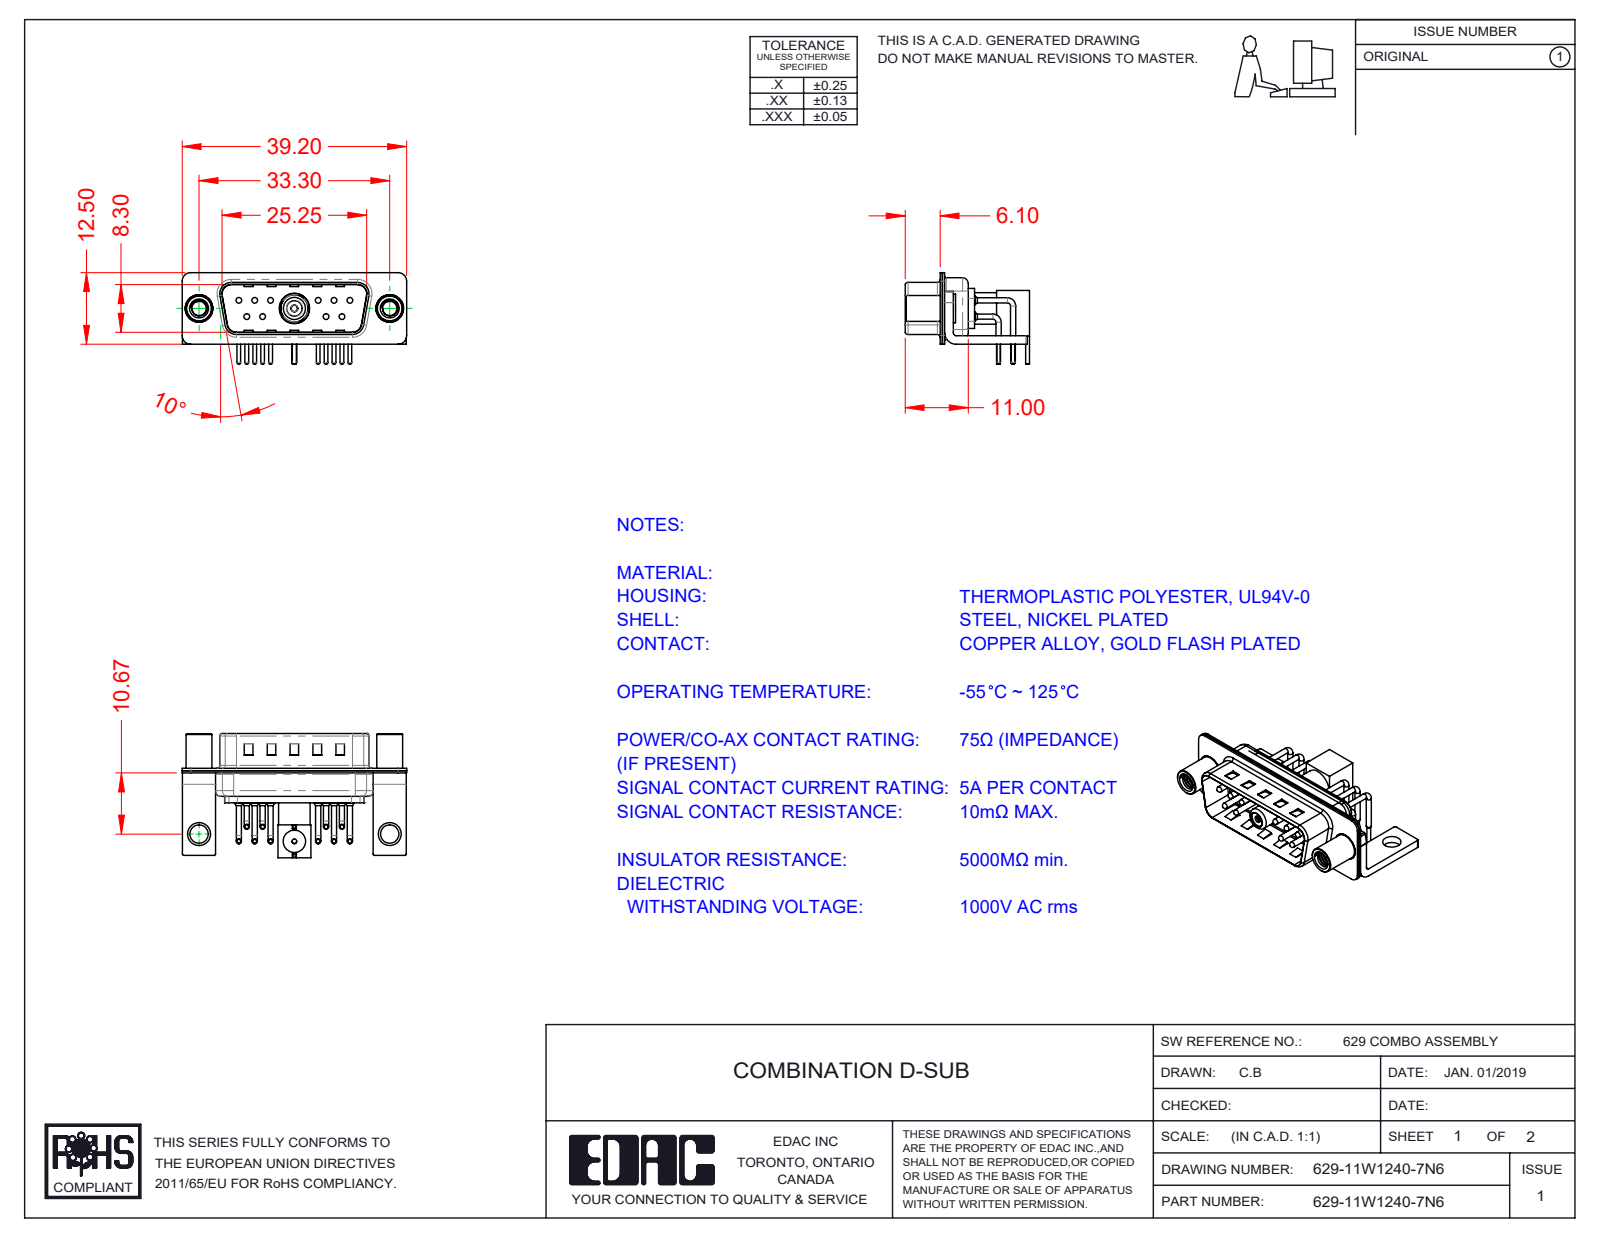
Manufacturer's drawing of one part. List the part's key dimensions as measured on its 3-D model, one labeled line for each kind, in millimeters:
Part name (STEP PRODUCT): Locking Collar; 629-11W1240-7N6; Socket_RA; Co-Ax Jack Assy_RA (+8 more)
STEP written by: SolidWorks 2020 (CONFIG_CONTROL_DESIGN)
Units: millimetres
Bodies: 24 solids, 1703 faces (867 planar, 636 cylindrical, 200 other)
Overall size (bounding box): 39.2 × 21.71 × 16
Volume: 2 595 mm³ · Surface area: 7 002 mm²
Round holes (diameter × count): ⌀1.6 ×11, ⌀0.75 ×10, ⌀2 ×10, ⌀2.5 ×3, ⌀3.2 ×2, ⌀4 ×2, ⌀4.8 ×2, ⌀0.8 ×1, ⌀1.1 ×1, ⌀1.2 ×1, ⌀1.5 ×1, ⌀2.7 ×1
Round bosses / shafts (diameter × count): ⌀0.9 ×20, ⌀1.5 ×10, ⌀1 ×10, ⌀0.65 ×10, ⌀5 ×2, ⌀4.9 ×2, ⌀4.5 ×2, ⌀0.8 ×2
Partial cylindrical surfaces — rounded edges, fillets, slot ends (radius × count): R0.25 ×16, R1.5 ×16, R2 ×13, R1.01 ×10, R0.5 ×9, R1.6 ×8, R1 ×7, R0.6 ×4
Main face-to-face distances: 0.4, 0.8, 1.5, 9.5, 9.1, 8.7, 9.9, 0.6, 1.9, 0.35
Hole centre spacings: 3.16, 2.77, 13.85, 16.7, 11.08, 16.62, 5.03, 5.04
